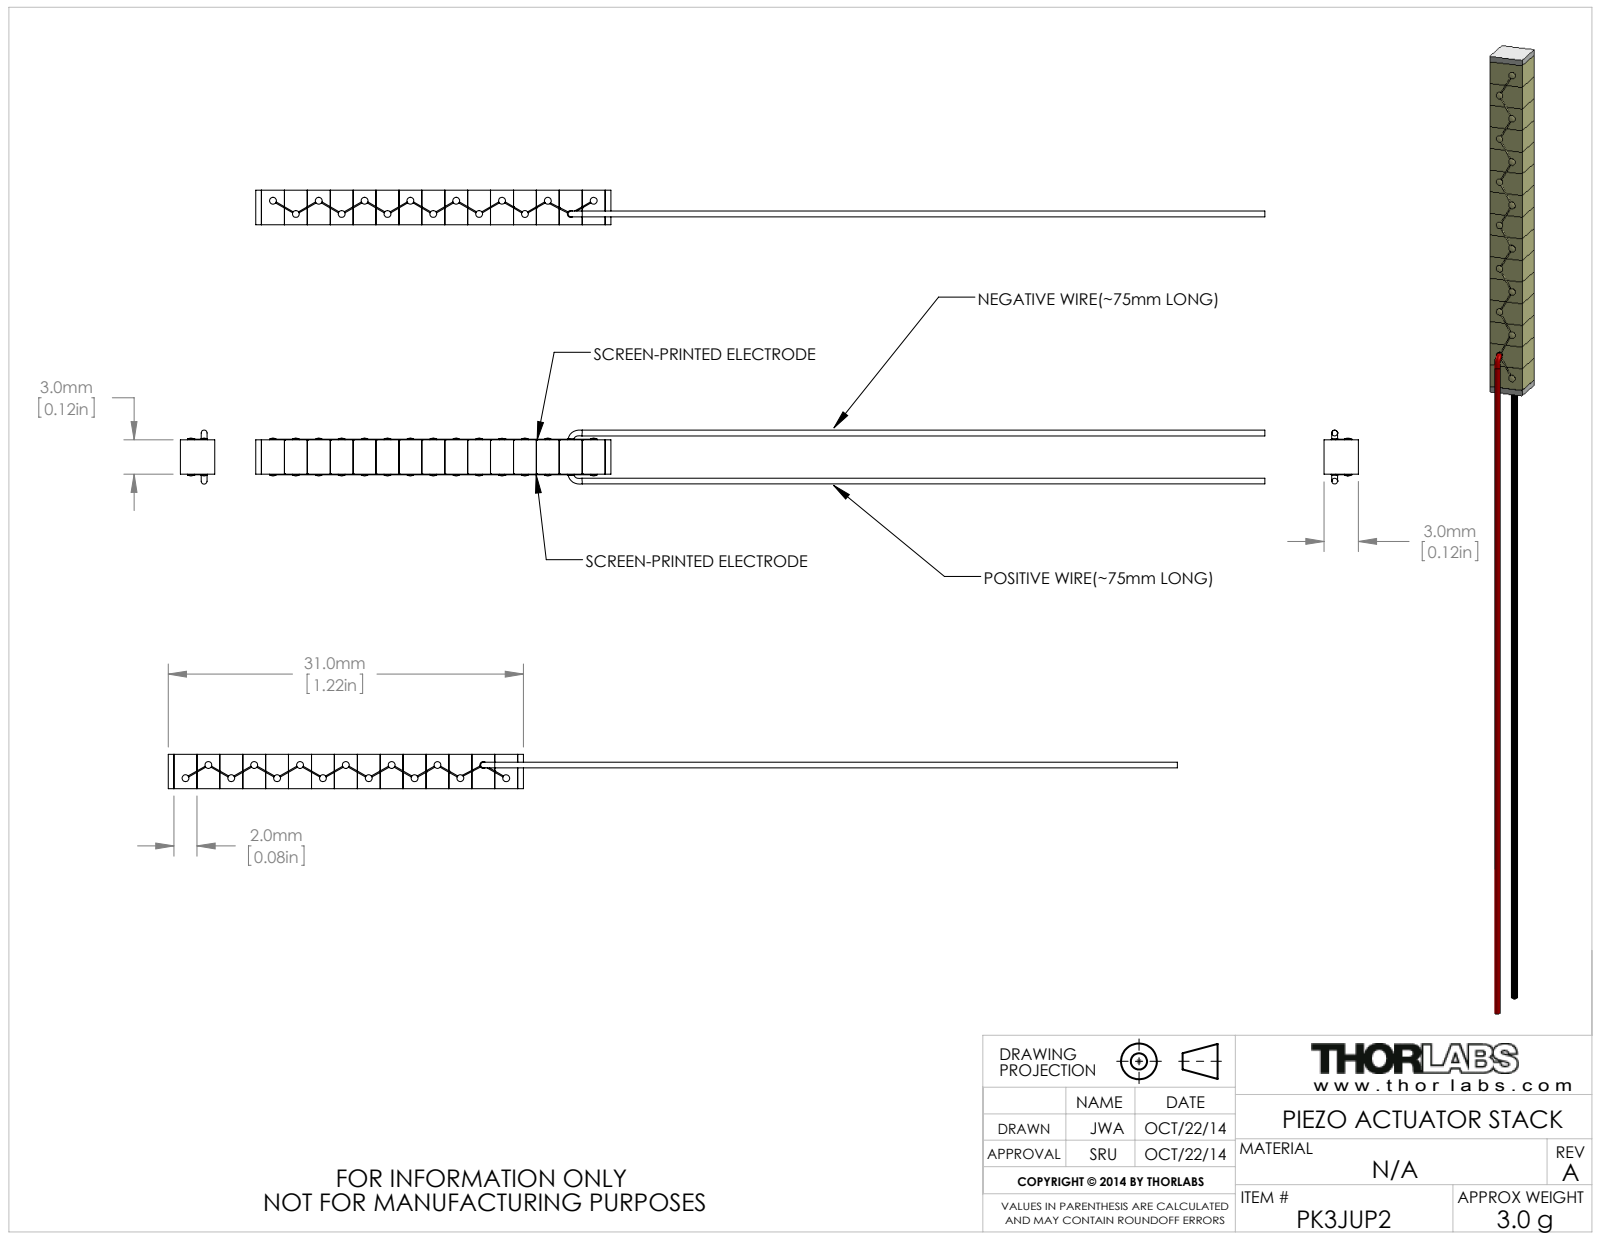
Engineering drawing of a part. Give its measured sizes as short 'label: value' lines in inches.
name: PK3JUP2
written by: SolidWorks 2012 (AUTOMOTIVE_DESIGN)
unit: in
bodies: 20 solids, 313 faces (121 planar, 126 cylindrical, 66 other)
size: 3.469 × 0.186 × 0.118
volume: 0.019 in³; area: 1.38 in²
bosses: 15× ⌀0.024
face distances: 0.079, 0.157, 0.236, 0.315, 0.394, 0.118, 0.472, 0.551, 0.63, 0.709
